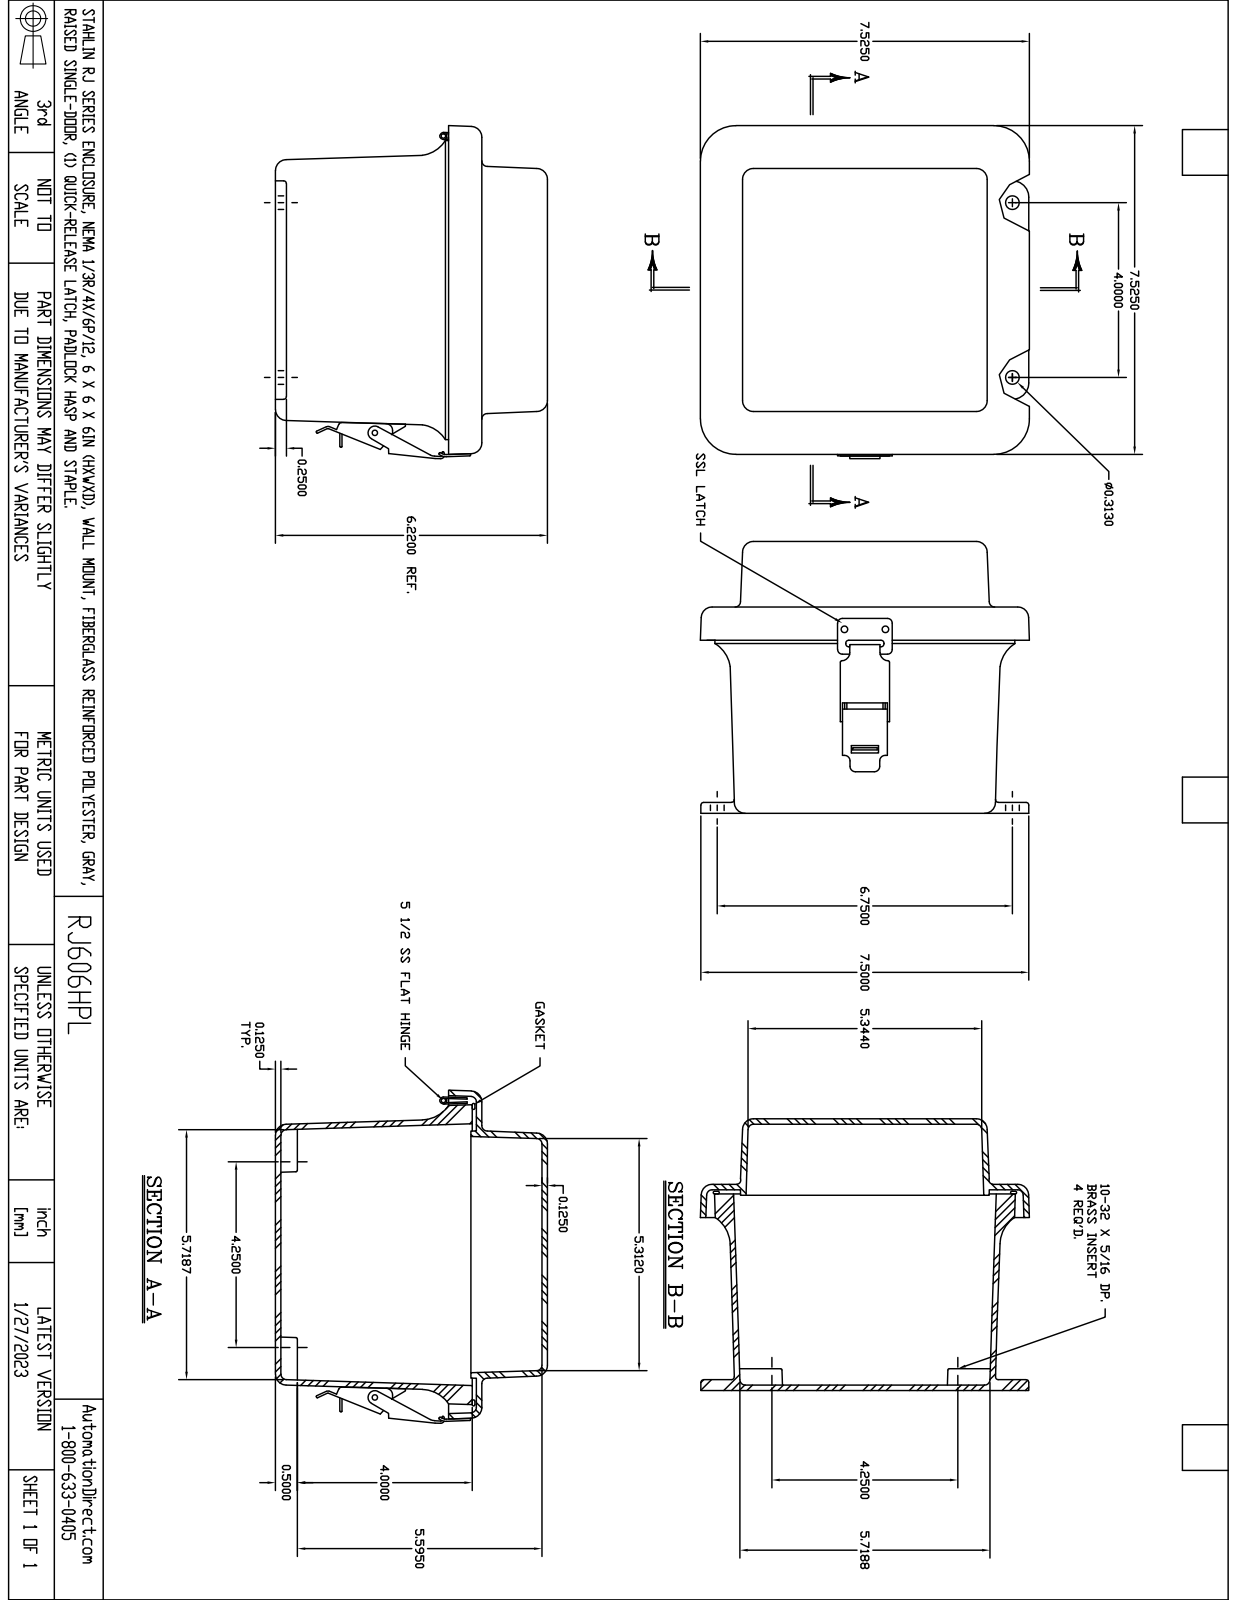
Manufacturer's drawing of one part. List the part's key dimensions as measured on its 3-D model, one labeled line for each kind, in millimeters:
Part name (STEP PRODUCT): MR606HPL
STEP written by: SolidWorks 2018 (AUTOMOTIVE_DESIGN)
Units: millimetres
Bodies: 25 solids, 698 faces (272 planar, 278 cylindrical, 148 other)
Overall size (bounding box): 193.4 × 191.1 × 161
Volume: 665 000 mm³ · Surface area: 374 600 mm²
Round holes (diameter × count): ⌀3.6 ×11, ⌀3.3 ×5, ⌀3.9 ×5, ⌀2.6 ×4, ⌀4 ×4, ⌀5.5 ×4, ⌀3.3 ×2, ⌀3.4 ×2, ⌀2.2 ×1, ⌀2.2 ×1, ⌀9.5 ×1
Round bosses / shafts (diameter × count): ⌀3.2 ×6, ⌀6.4 ×5, ⌀6.9 ×4, ⌀3.2 ×3, ⌀7.6 ×1, ⌀4.3 ×1, ⌀3.9 ×1, ⌀3.9 ×1
Partial cylindrical surfaces — rounded edges, fillets, slot ends (radius × count): R0.8 ×20, R3.2 ×20, R6.4 ×16, R0.4 ×12, R1.1 ×8, R0.8 ×6, R0.6 ×5, R1.5 ×4
Main face-to-face distances: 3.2, 3.2, 38.1, 116.5, 154.6, 157.8, 161, 157.8, 119.7, 41.3
Hole centre spacings: 134.8, 23.8, 34.8, 63.5, 108, 157.1, 187.5, 19.1
